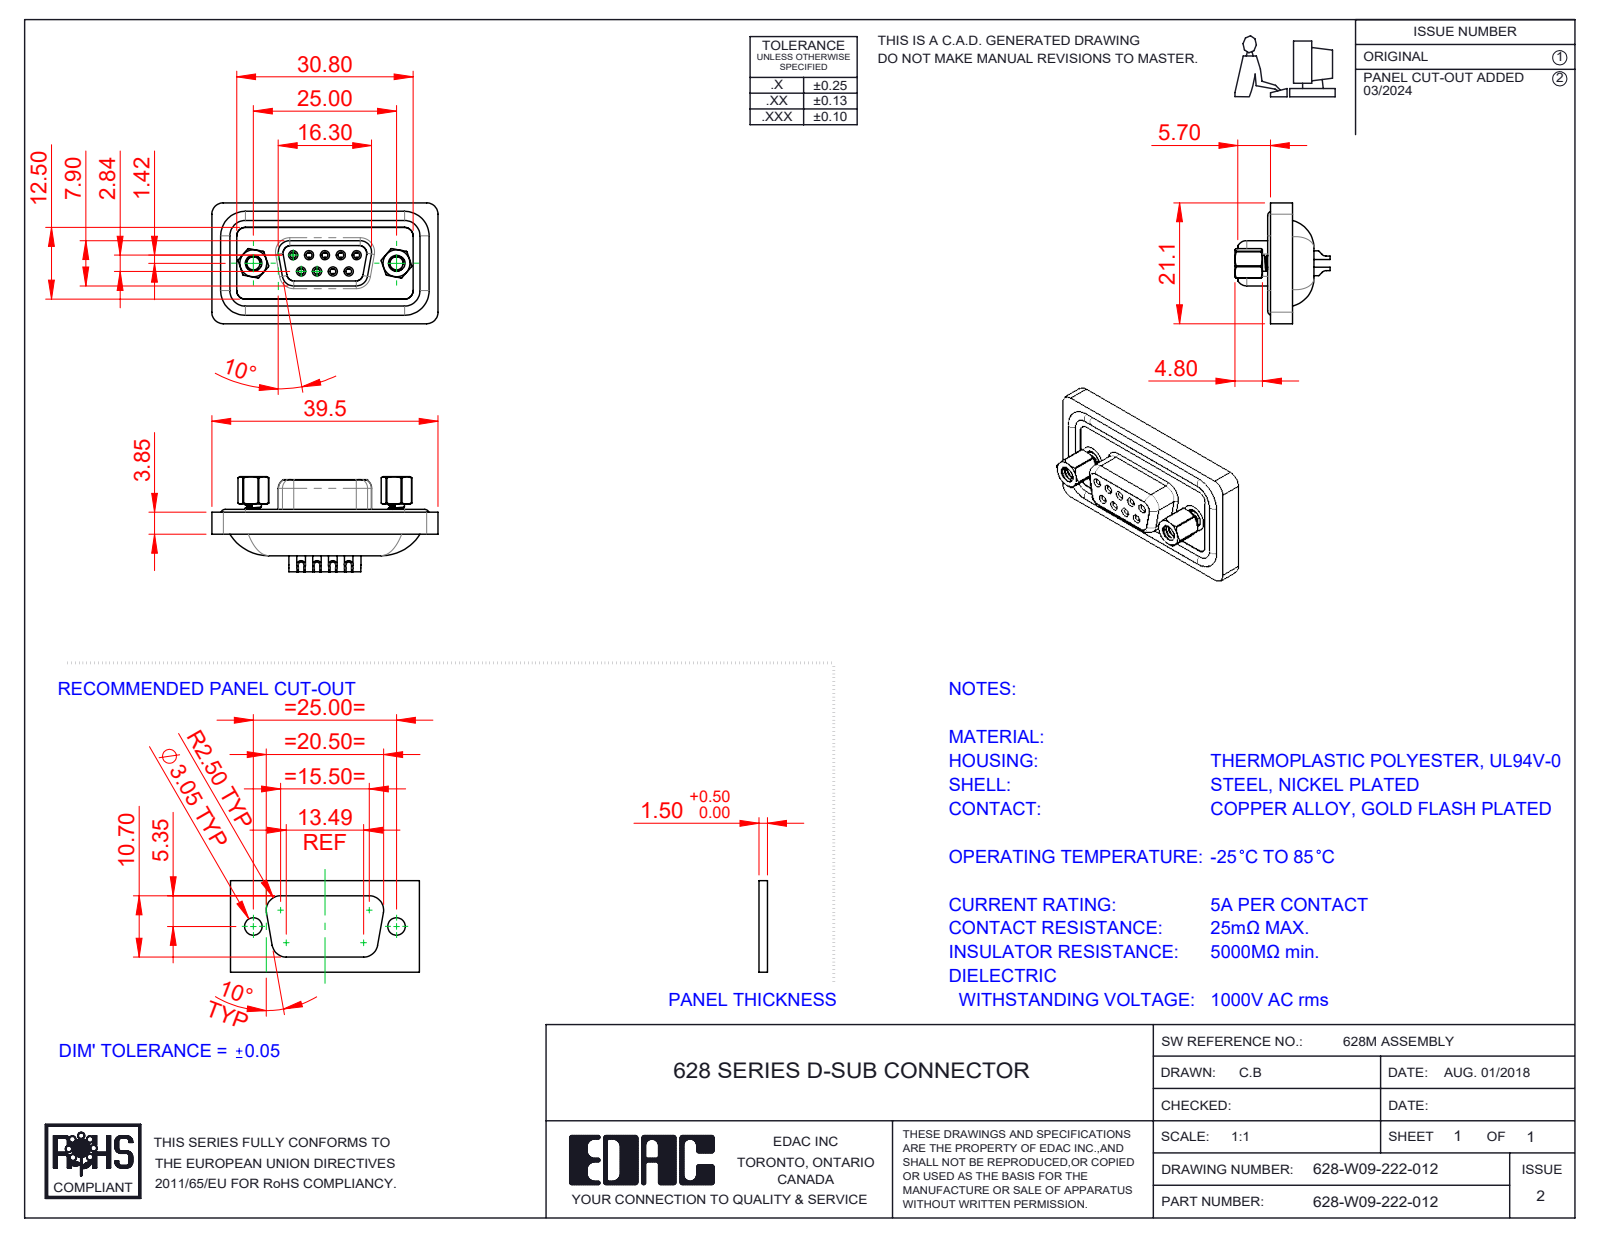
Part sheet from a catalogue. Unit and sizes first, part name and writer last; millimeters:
Units: millimetres
Overall size (bounding box): 39.5 × 21.1 × 16.1
Round holes (diameter × count): ⌀1 ×9, ⌀1.1 ×9, ⌀1.5 ×9, ⌀1.7 ×9, ⌀1.8 ×9, ⌀2 ×9, ⌀2.26 ×2, ⌀2.29 ×2, ⌀4 ×2, ⌀4.8 ×2, ⌀5 ×2
Round bosses / shafts (diameter × count): ⌀1.6 ×13, ⌀2.2 ×9, ⌀4.9 ×2, ⌀2.79 ×2
Partial cylindrical surfaces — rounded edges, fillets, slot ends (radius × count): R2 ×16, R1.5 ×14, R1.35 ×8, R2.7 ×6, R0.5 ×4, R0.9 ×4, R1.6 ×4, R1.75 ×4
Main face-to-face distances: 0.4, 1.1, 2.75, 0.5, 3.75, 1, 3.5, 3.35, 3.85, 7.5
Hole centre spacings: 3.16, 2.77, 5.54, 5.03, 5.04, 8.31, 7.1, 7.48
Volume: 5 039 mm³ · Surface area: 7 495 mm²
Bodies: 17 solids, 936 faces (254 planar, 427 cylindrical, 255 other)
Part name (STEP PRODUCT): 628W Contact Row 1_22; 628-W09-222-012; 628W 4-40 Threaded Rivet; 628W Waterproof Housing_09 Contacts (+4 more)
STEP written by: SolidWorks 2020 (CONFIG_CONTROL_DESIGN)
